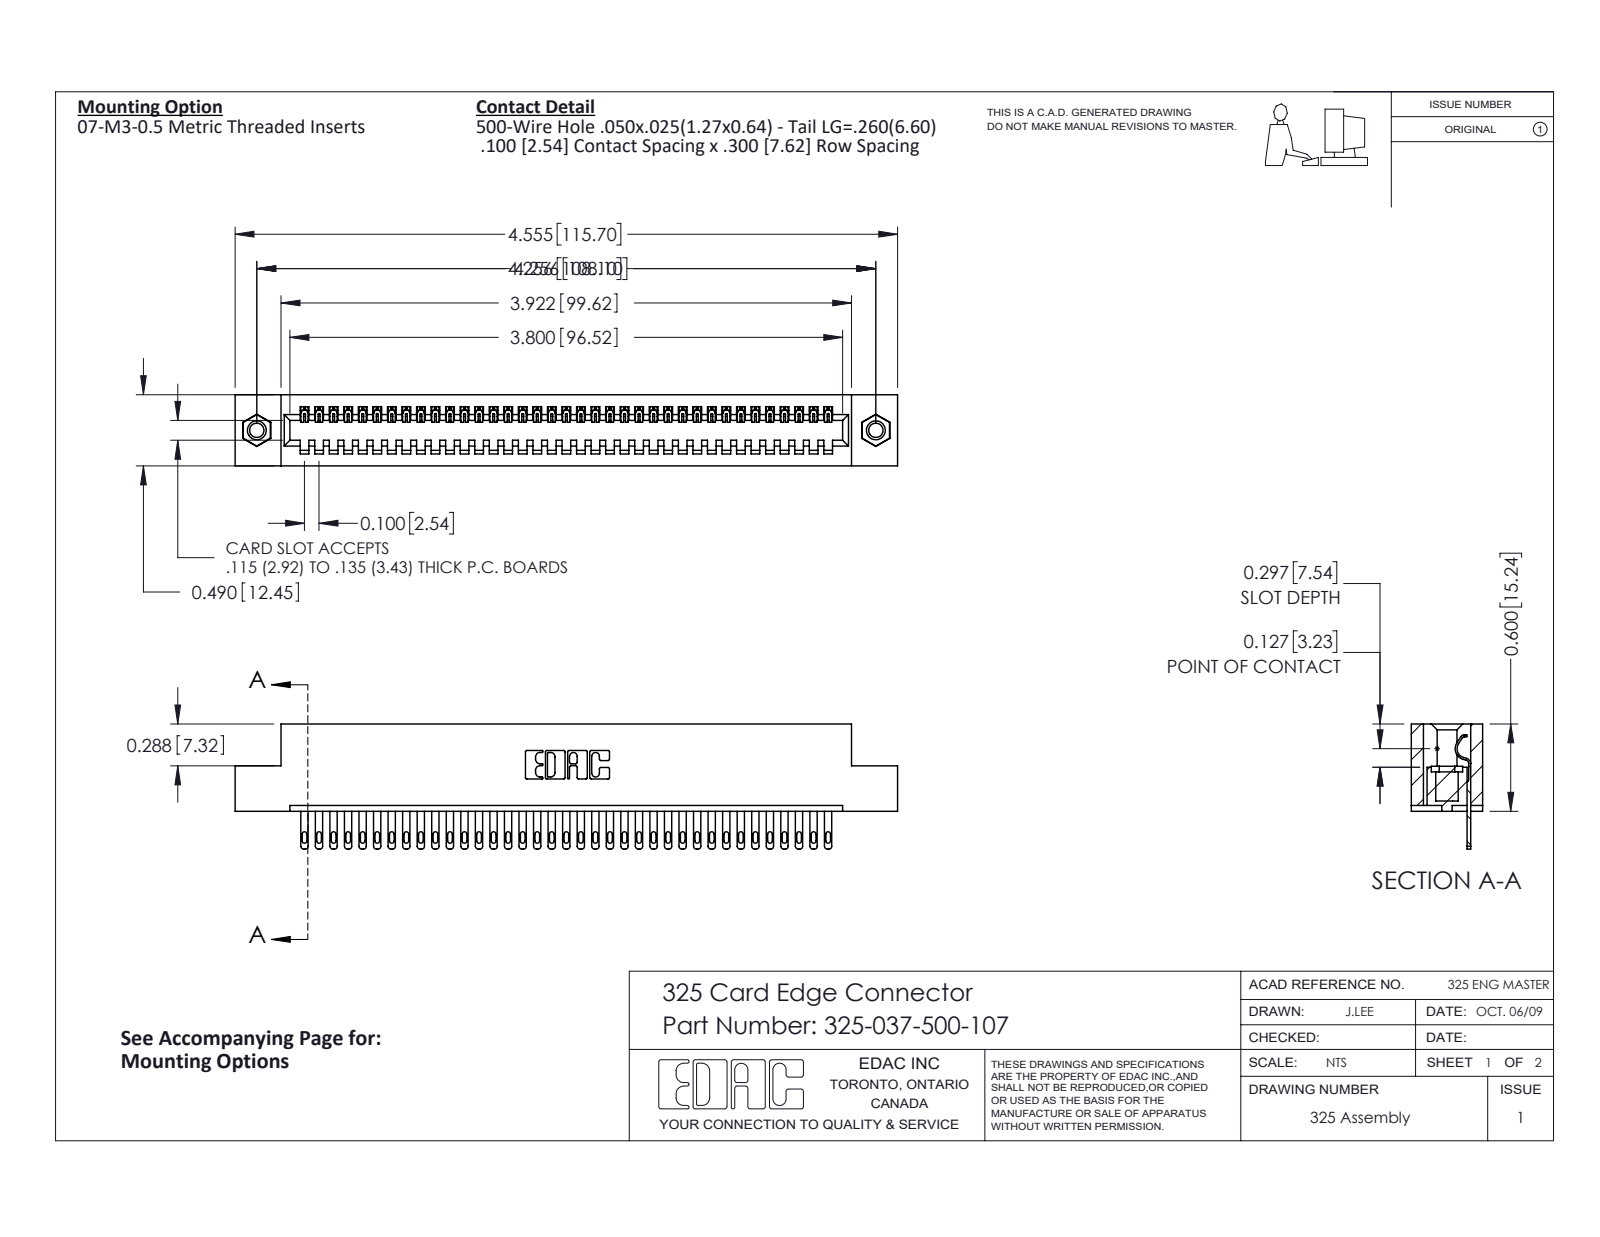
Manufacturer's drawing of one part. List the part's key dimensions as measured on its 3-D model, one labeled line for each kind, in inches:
Part name (STEP PRODUCT): 345-250-001_345-250-005-103; 325-292-001_325-293-100; 325 Part_TI; 325-037-500-107
STEP written by: SolidWorks 2016 (CONFIG_CONTROL_DESIGN)
Units: inches
Bodies: 40 solids, 2172 faces (1434 planar, 722 cylindrical, 16 other)
Overall size (bounding box): 4.555 × 0.86 × 0.49
Volume: 0.894 in³ · Surface area: 24.87 in²
Round holes (diameter × count): ⌀0.098 ×2, ⌀0.125 ×2, ⌀0.16 ×2
Round bosses / shafts (diameter × count): ⌀0.155 ×2
Partial cylindrical surfaces — rounded edges, fillets, slot ends (radius × count): R0.006 ×74, R0.016 ×74, R0.02 ×74, R0.01 ×22, R0.007 ×6, R0.031 ×6, R0.026 ×3, R0.014 ×1
Main face-to-face distances: 0.083, 0.407, 0.49, 0.3, 0.107, 0.383, 0.025, 0.325, 0.56, 0.263
Hole centre spacings: 4.256
